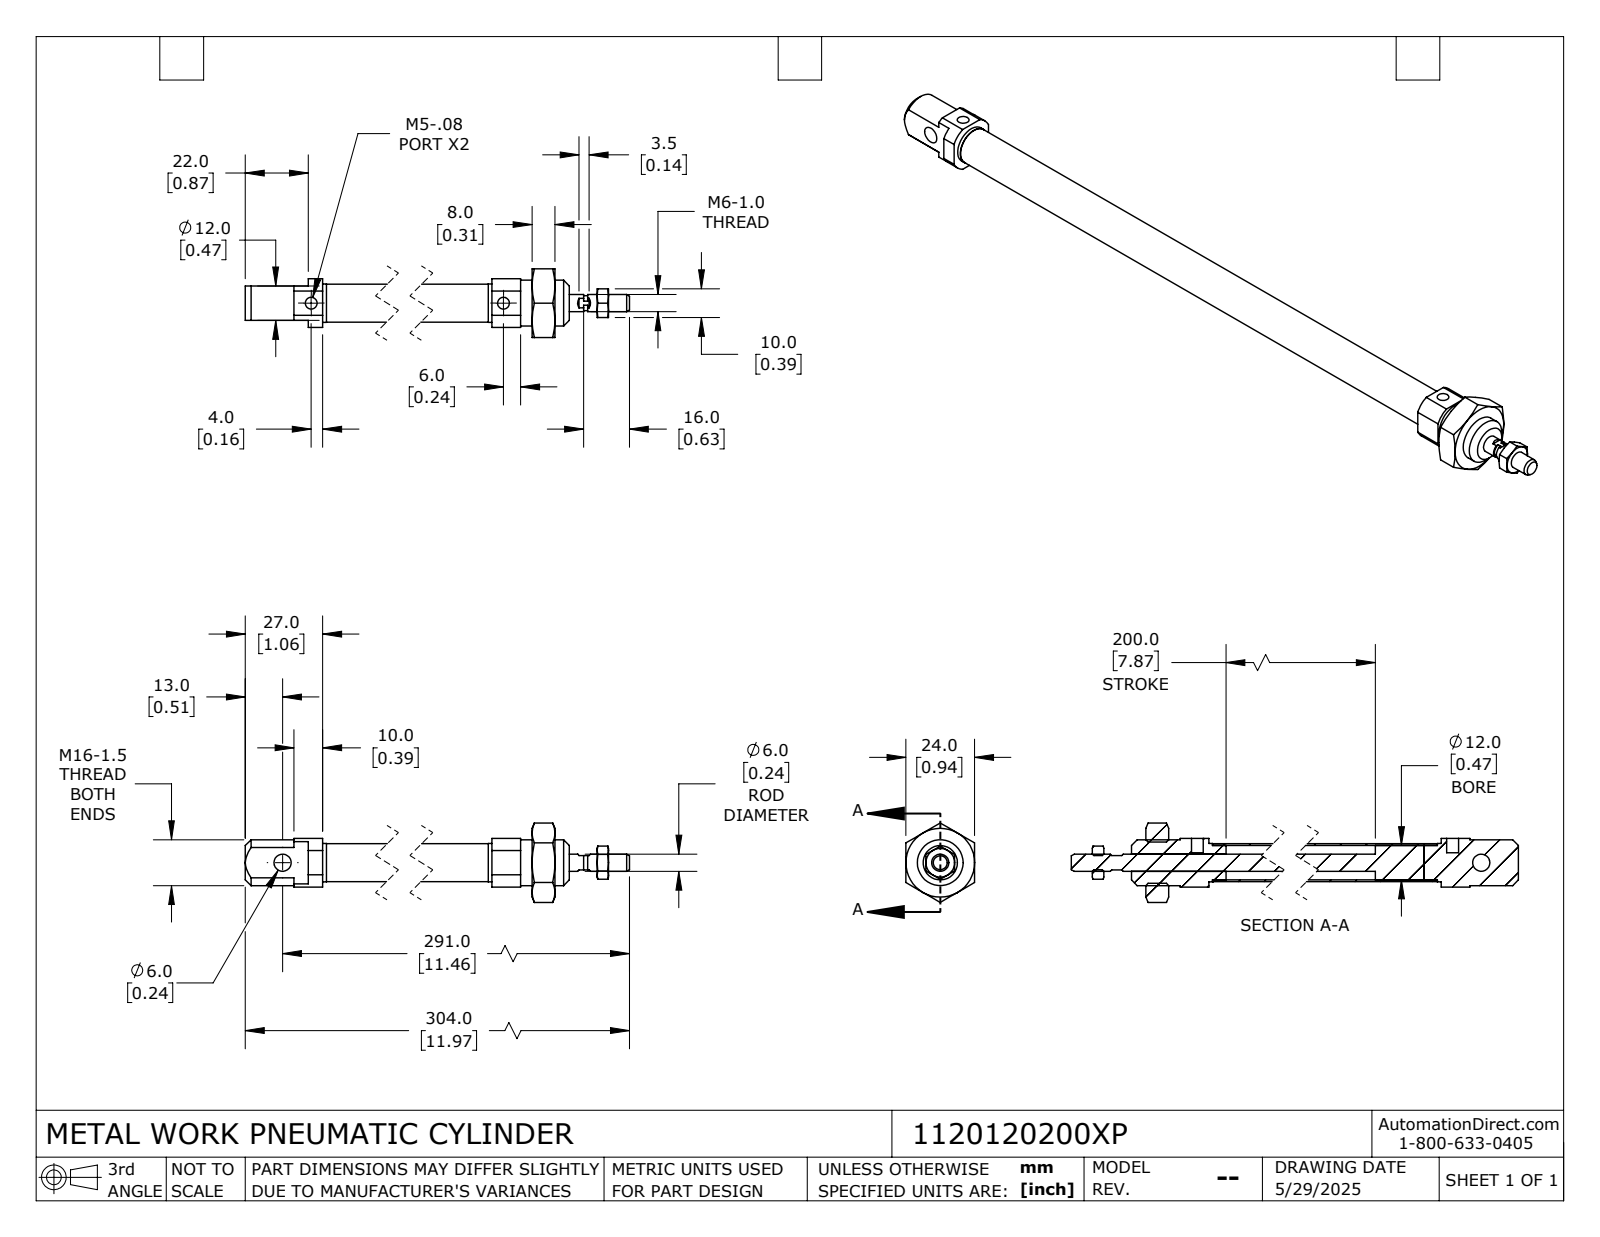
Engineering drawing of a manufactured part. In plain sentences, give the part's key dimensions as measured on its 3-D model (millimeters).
The part is named "1120120200XP; 1120120200XP_BODY; 1120120200XP_ROD". Its 3-D file was written by "SolidWorks 2024 (CONFIG_CONTROL_DESIGN)". It is 6 solids with 139 faces: 56 planar, 45 cylindrical and 38 other. Overall it measures 304 by 27.71 by 24 millimeters. Its volume is 28 822 cubic millimeters and its surface area 30 709 square millimeters. Round holes: 2 of diameter 4.13, 1 of diameter 4.92, 1 of diameter 6, 1 of diameter 14.38. Round bosses or shafts: 1 of diameter 16, 1 of diameter 13.4, 1 of diameter 13.27, 1 of diameter 12, 1 of diameter 6, 1 of diameter 5.2. Partial cylindrical surfaces (rounded edges, fillets, slot ends): 1 of radius 9.5. The main face-to-face distances are 17, 6, 24, 12, 256, 2.5, 14.5, 8, 3.5, 33. The hole center spacings are 237.
